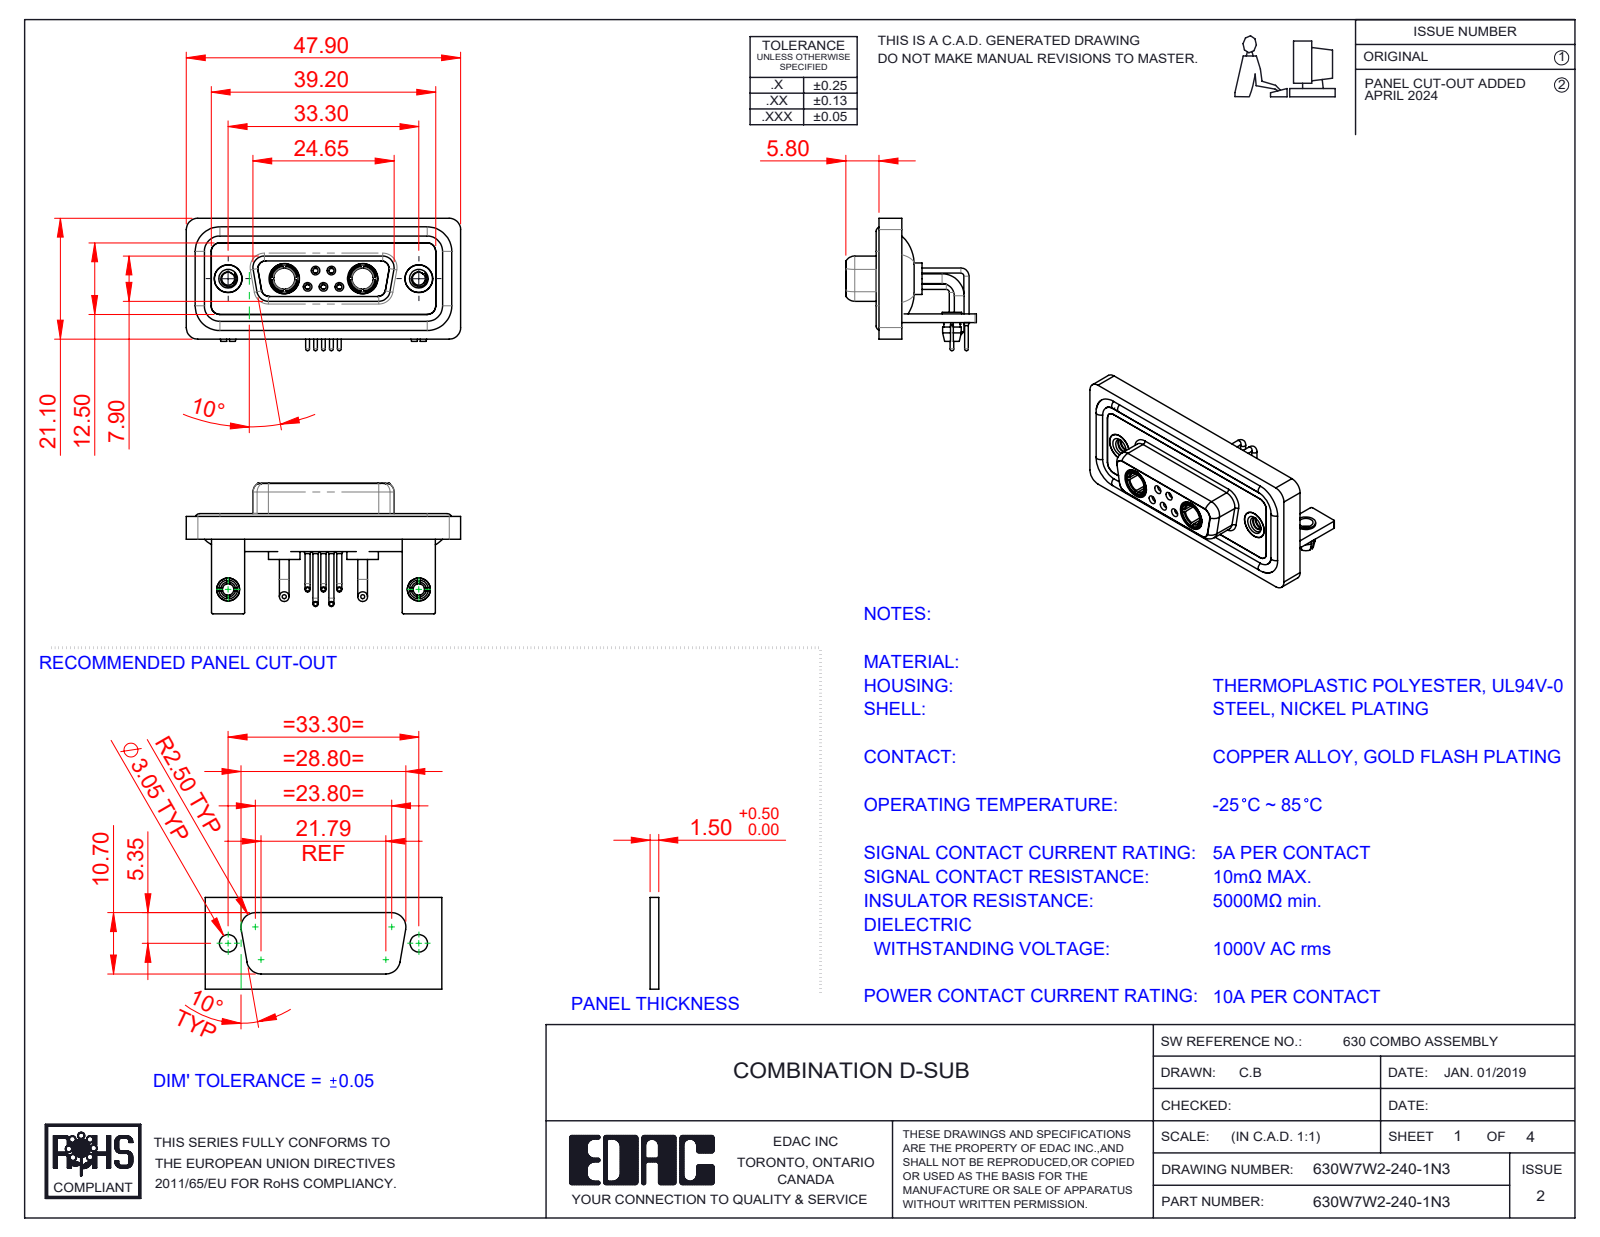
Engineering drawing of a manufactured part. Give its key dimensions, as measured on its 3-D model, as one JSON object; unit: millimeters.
{"part_name": "630Combo Housing_7W2; Power Socket_10A RA; 630W7W2-240-1N3; 630Combo Threaded Rivet_2 (+7 more)", "step_written_by": "SolidWorks 2023 (CONFIG_CONTROL_DESIGN)", "units": "millimeters", "bodies": {"solids": 20, "faces": 947, "planar": 306, "cylindrical": 409, "other": 232}, "overall_size": [47.9, 23.12, 22.8], "volume_mm3": 6483, "surface_area_mm2": 11050, "round_holes": [[2, 7], [0.9, 5], [1.1, 5], [1.5, 5], [4.85, 4], [1.6, 3], [1.7, 2], [2.26, 2], [2.5, 2], [3.2, 2], [3.7, 2], [4, 2]], "round_bosses_or_shafts": [[1.6, 6], [0.9, 5], [0.65, 5], [1.7, 4], [5.5, 2], [5.2, 2], [4.96, 2], [4.95, 2]], "partial_cylinders_radius": [[2, 21], [1.5, 18], [0.25, 16], [1.35, 12], [1.6, 8], [0.5, 5], [0.6, 4], [0.65, 4]], "face_to_face_distances": [0.4, 2.9, 1.5, 1.8, 3.7, 1.1, 4.1, 1.6, 2.5, 1.4], "hole_center_spacings": [3.16, 2.77, 9.8, 23.5, 33.3, 4.31, 4.33, 5.03]}
